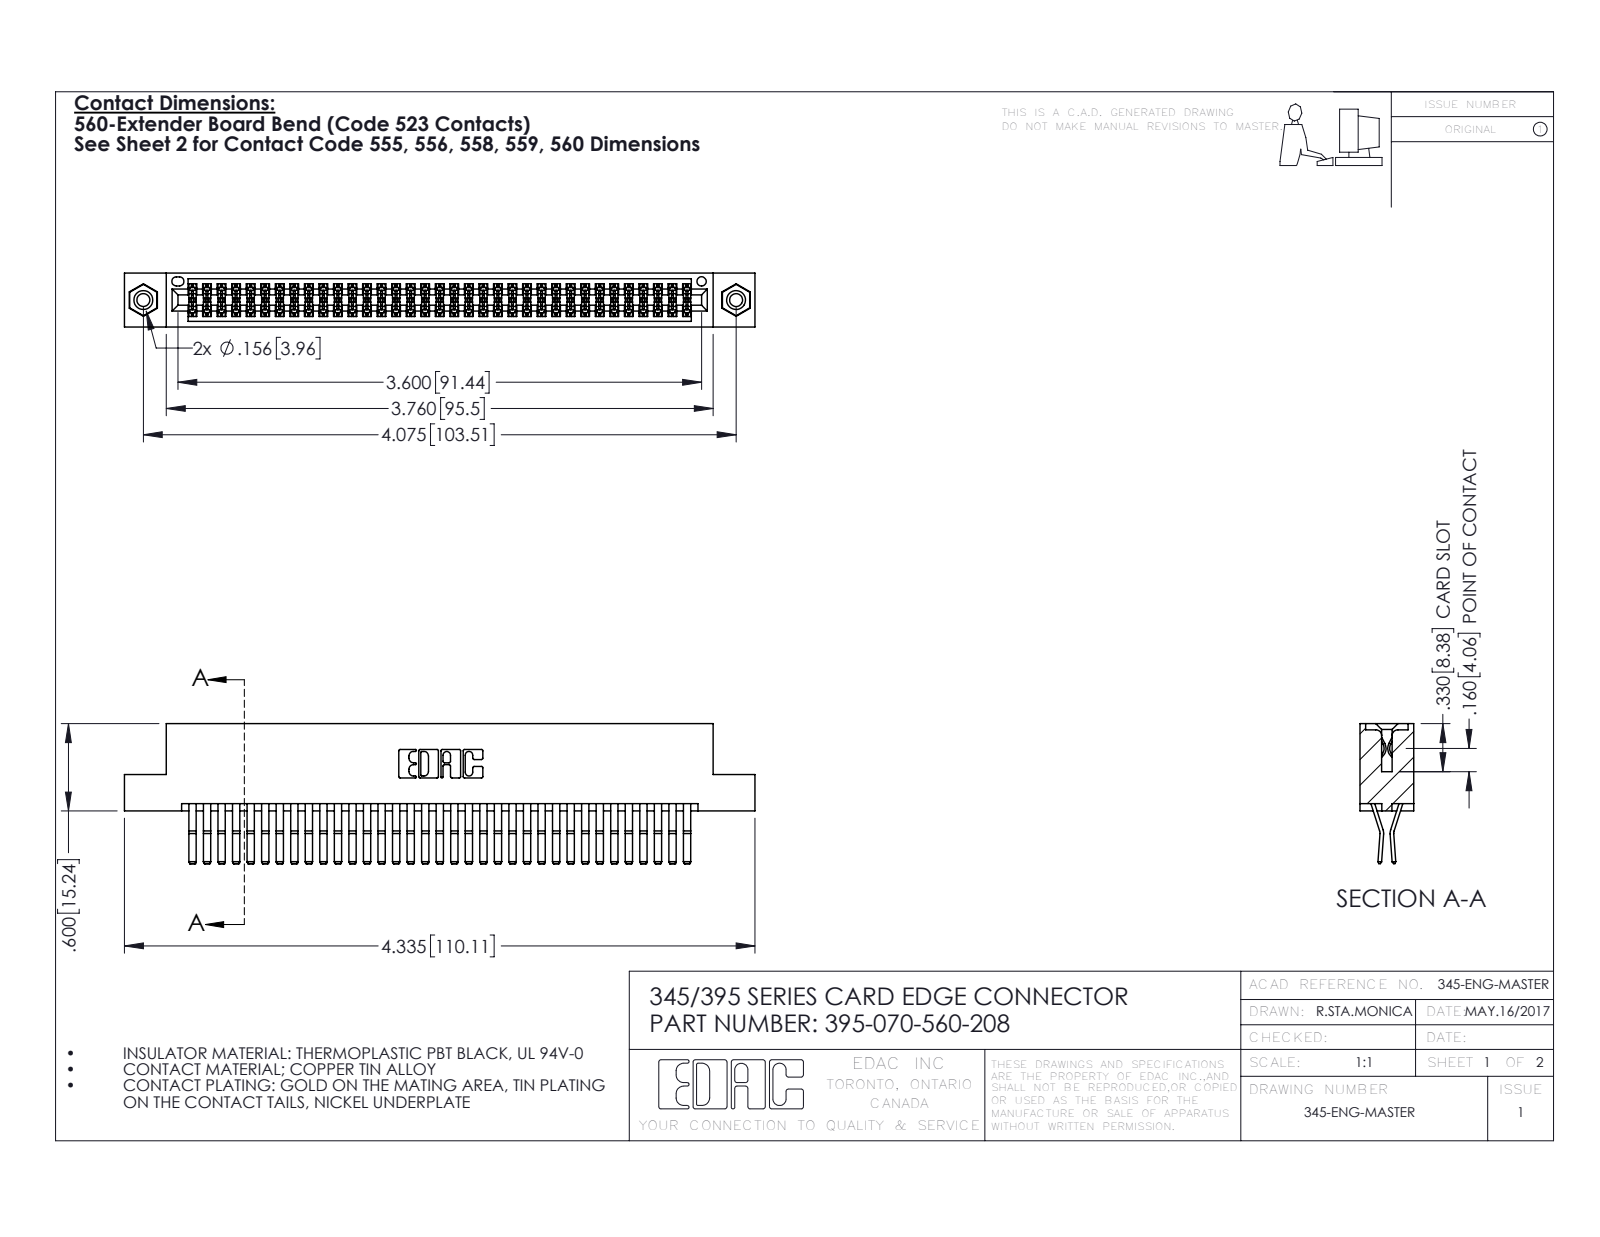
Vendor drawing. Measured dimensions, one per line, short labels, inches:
name: 345-292-001_560 Tail; 345-250-001_345-250-003-102; 345 Part_Flush Mounting Lugs - 0.156 Dia-TI; 395-070-560-208
written by: SolidWorks 2016 (CONFIG_CONTROL_DESIGN)
unit: in
bodies: 73 solids, 3826 faces (2422 planar, 1388 cylindrical, 16 other)
size: 4.335 × 0.962 × 0.37
volume: 0.676 in³; area: 27.03 in²
holes: 2× ⌀0.089, 2× ⌀0.125, 2× ⌀0.156, 1× ⌀0.064
bosses: 2× ⌀0.155
rounds: 105× R0.006, 22× R0.01, 6× R0.007, 6× R0.031, 3× R0.026, 2× R0.01, 2× R0.014, 2× R0.019
face distances: 0.025, 0.072, 0.298, 0.37, 0.2, 0.098, 0.272, 0.225, 0.175, 0.149
hole spacings: 0.27, 3.839, 4.075
